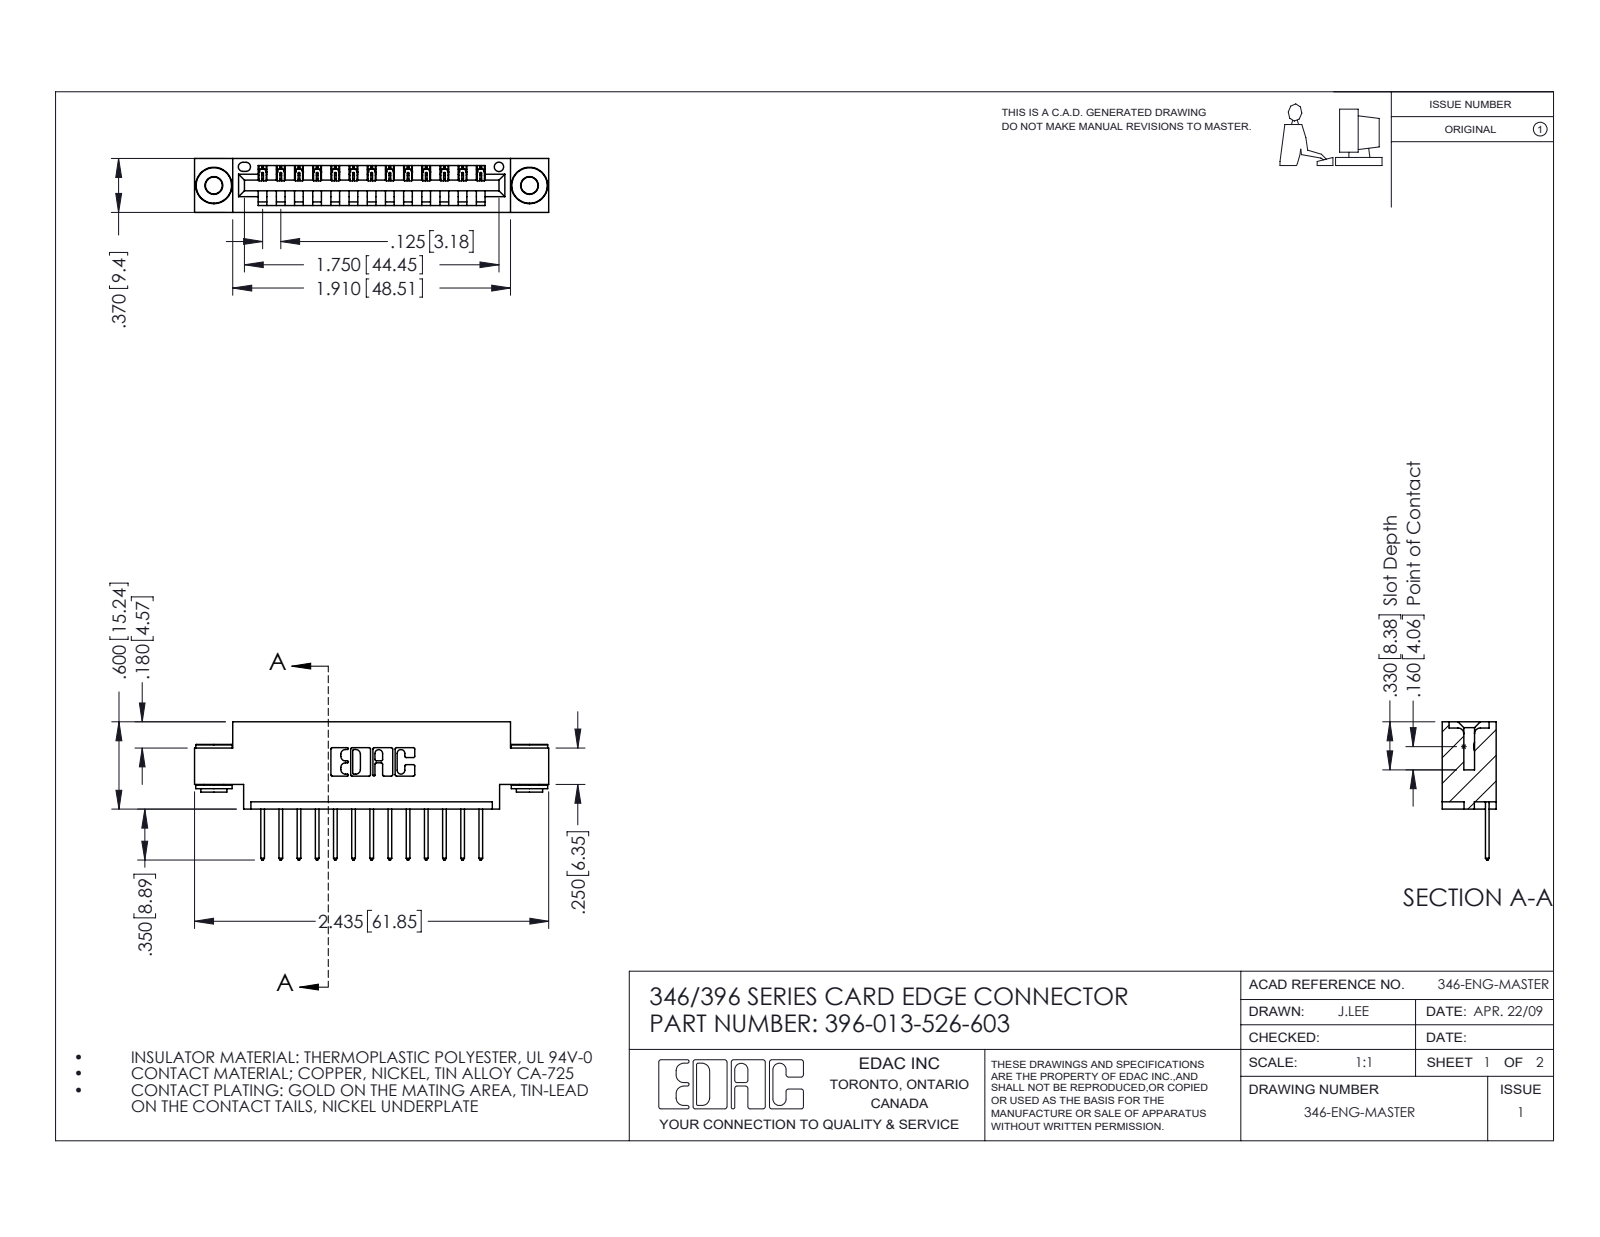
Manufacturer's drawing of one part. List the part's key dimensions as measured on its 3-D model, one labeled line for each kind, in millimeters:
Part name (STEP PRODUCT): 345-250-002_345-250-002-102; 345-292-001_345-293-126; 346 Part_0.170 Offset - 0.156 Dia-TH; 396-013-526-603
STEP written by: SolidWorks 2016 (CONFIG_CONTROL_DESIGN)
Units: millimetres
Bodies: 16 solids, 918 faces (610 planar, 300 cylindrical, 8 other)
Overall size (bounding box): 61.8 × 24.1 × 9.4
Volume: 5 570 mm³ · Surface area: 7 019 mm²
Round holes (diameter × count): ⌀2.9 ×2, ⌀4 ×2, ⌀1.6 ×1
Round bosses / shafts (diameter × count): ⌀6.4 ×2, ⌀4.6 ×2, ⌀3.5 ×2
Partial cylindrical surfaces — rounded edges, fillets, slot ends (radius × count): R0.2 ×26, R0.3 ×26, R0.3 ×22, R0.2 ×6, R0.8 ×6, R0.7 ×3, R0.8 ×2, R1 ×2
Main face-to-face distances: 6.4, 9.4, 1.2, 8.2, 0.6, 1.8, 7.6, 3.8, 5.6, 2.5
Hole centre spacings: 6.2, 49.9, 55.1
